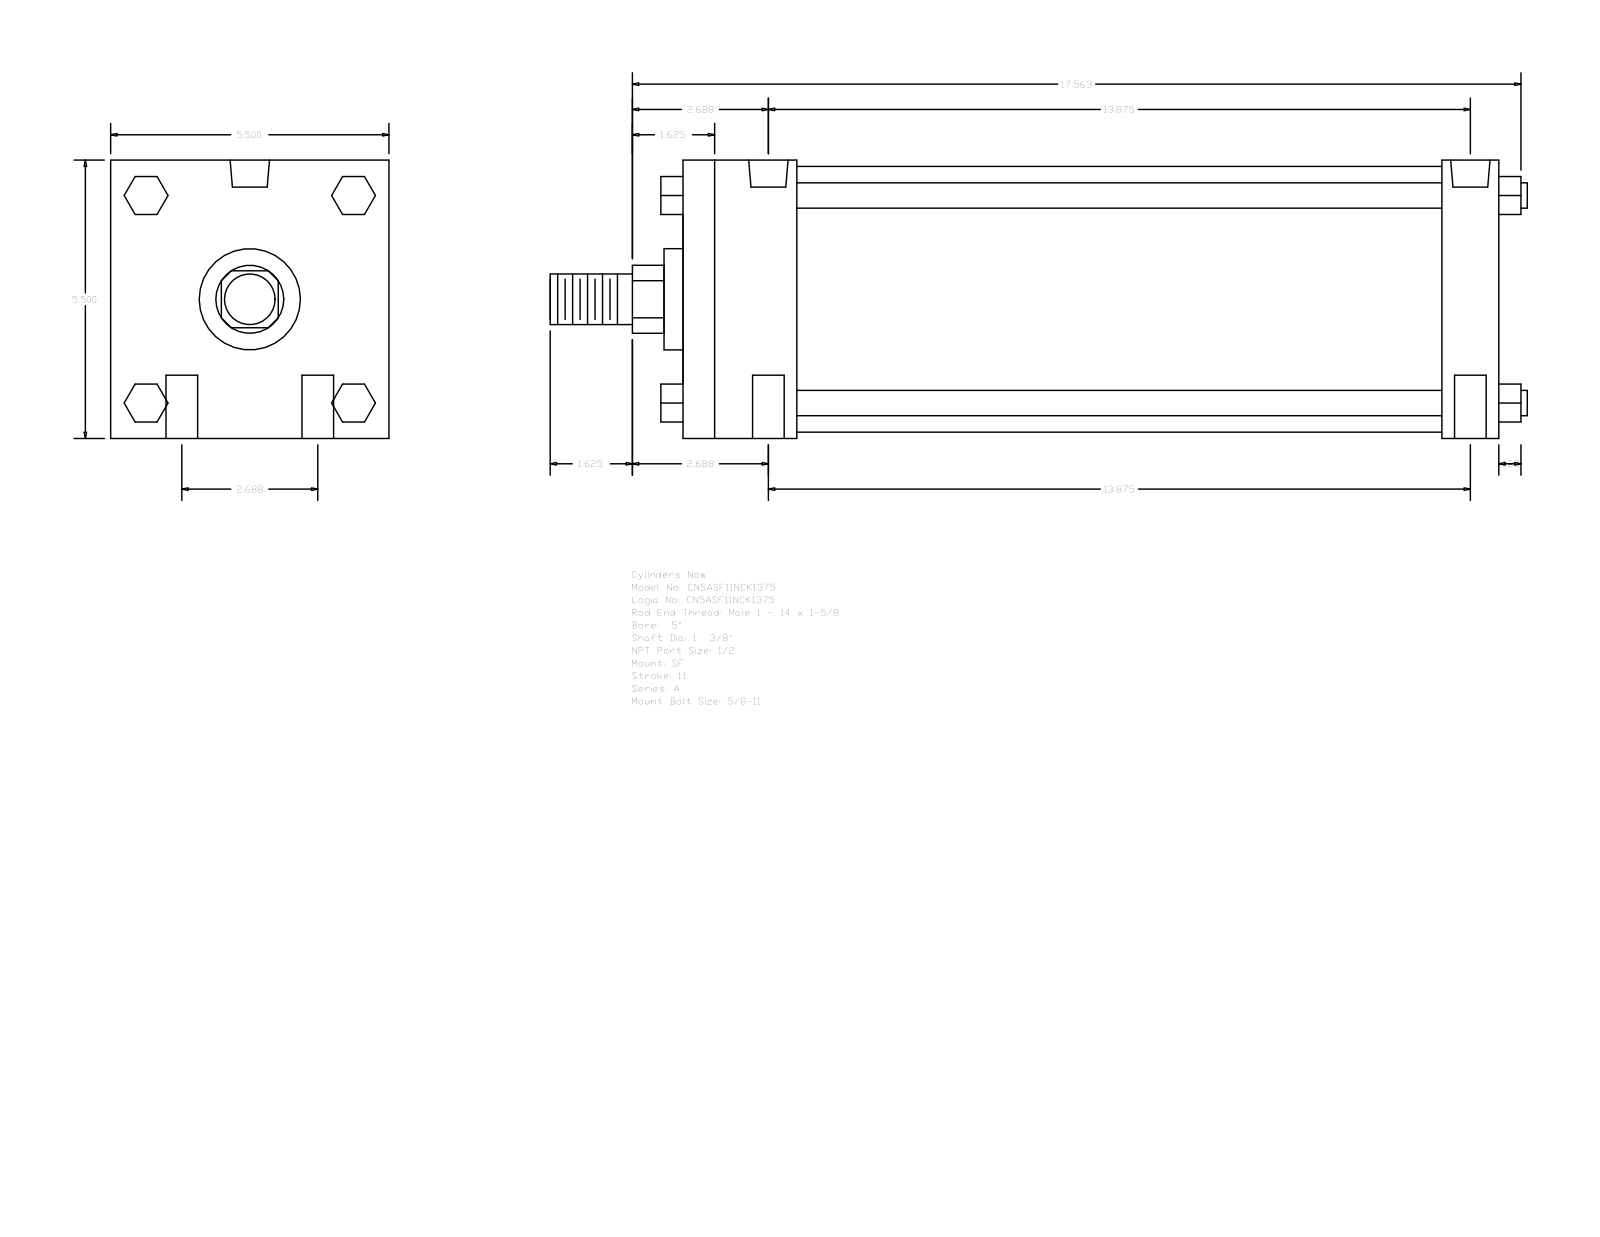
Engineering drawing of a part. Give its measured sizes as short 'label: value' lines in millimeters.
name: A_SF__0500_1.375
written by: GSSL Pune (CONFIG_CONTROL_DESIGN)
unit: mm
bodies: 0 solids, 124 faces (94 planar, 30 cylindrical, 0 other)
size: 490.54 × 139.7 × 139.7
holes: 4× ⌀15.88, 2× ⌀8.73, 2× ⌀19.77
bosses: 4× ⌀12.7, 1× ⌀133.35, 1× ⌀50.8, 1× ⌀34.92, 1× ⌀25.4
rounds: 1× R17.06
face distances: 139.7, 409.58, 57.15, 28.58, 381, 323.85, 352.43, 19.05, 52.07, 90.18
hole spacings: 34.13, 354.08, 352.43, 68.26, 358.98, 347.65
